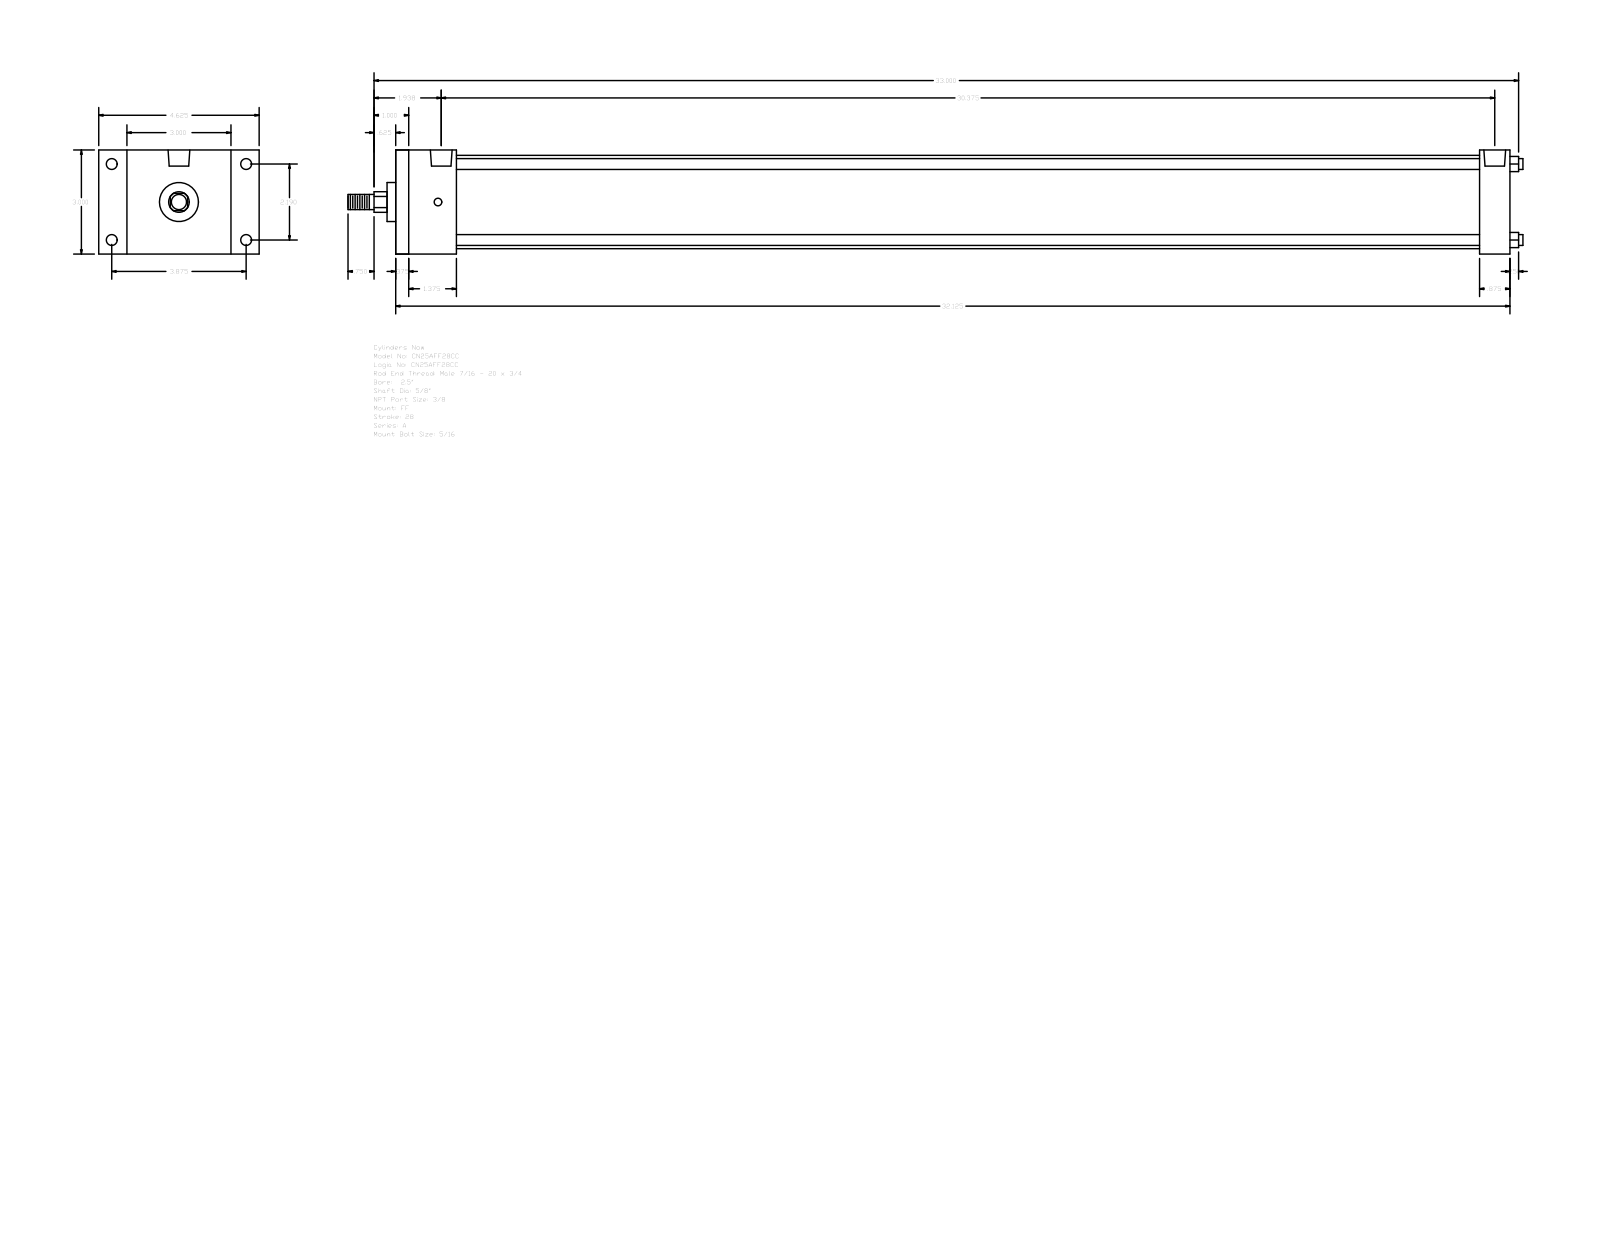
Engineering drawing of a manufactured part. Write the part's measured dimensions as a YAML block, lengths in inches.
part_name: "A_FF__0250_0.625"
step_written_by: "GSSL Pune (CONFIG_CONTROL_DESIGN)"
units: inches
bodies: {solids: 0, faces: 92, planar: 64, cylindrical: 28, other: 0}
overall_size: [33.875, 4.625, 3]
round_holes:
  - {diameter: 0.219, count: 4}
  - {diameter: 0.313, count: 4}
  - {diameter: 0.627, count: 2}
round_bosses_or_shafts:
  - {diameter: 0.313, count: 4}
  - {diameter: 2.69, count: 1}
  - {diameter: 1.125, count: 1}
  - {diameter: 0.625, count: 1}
  - {diameter: 0.437, count: 1}
partial_cylinders:
  - {radius: 0.297, count: 1}
face_to_face_distances: [3, 32.125, 0.375, 31.75, 1.75, 1.375, 31.25, 30.875, 29.5, 30.375]
hole_center_spacings: [0.094, 2.19, 3.875, 4.451, 30.469, 30.563, 30.375]
